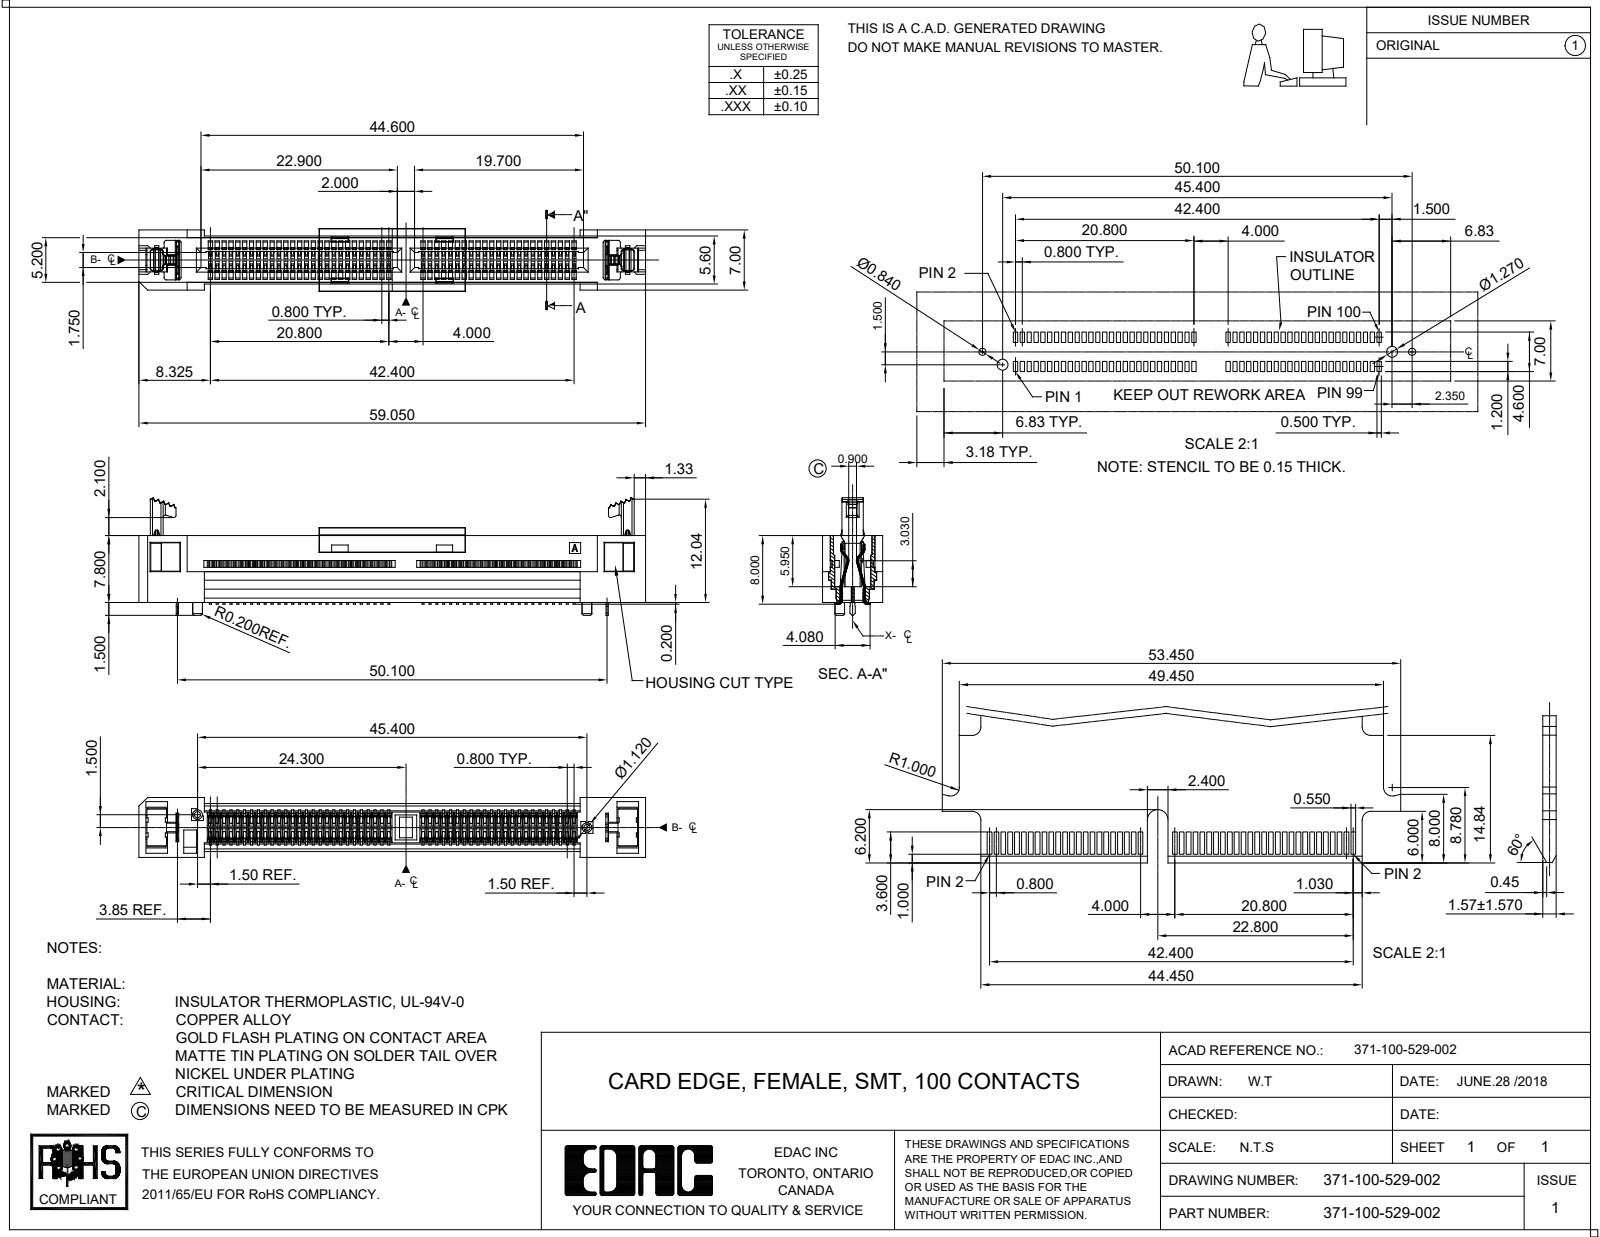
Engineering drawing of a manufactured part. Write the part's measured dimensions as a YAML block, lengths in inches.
part_name: "371-100-529-002"
step_written_by: "SolidWorks 2020 (AUTOMOTIVE_DESIGN)"
units: inches
bodies: {solids: 0, faces: 8202, planar: 5362, cylindrical: 0, other: 2840}
overall_size: [2.325, 0.54, 0.276]
face_to_face_distances: [0.098, 0.177, 0.142, 0.063, 0.035, 0.24, 0.276, 0.079, 0.307, 0.205]
